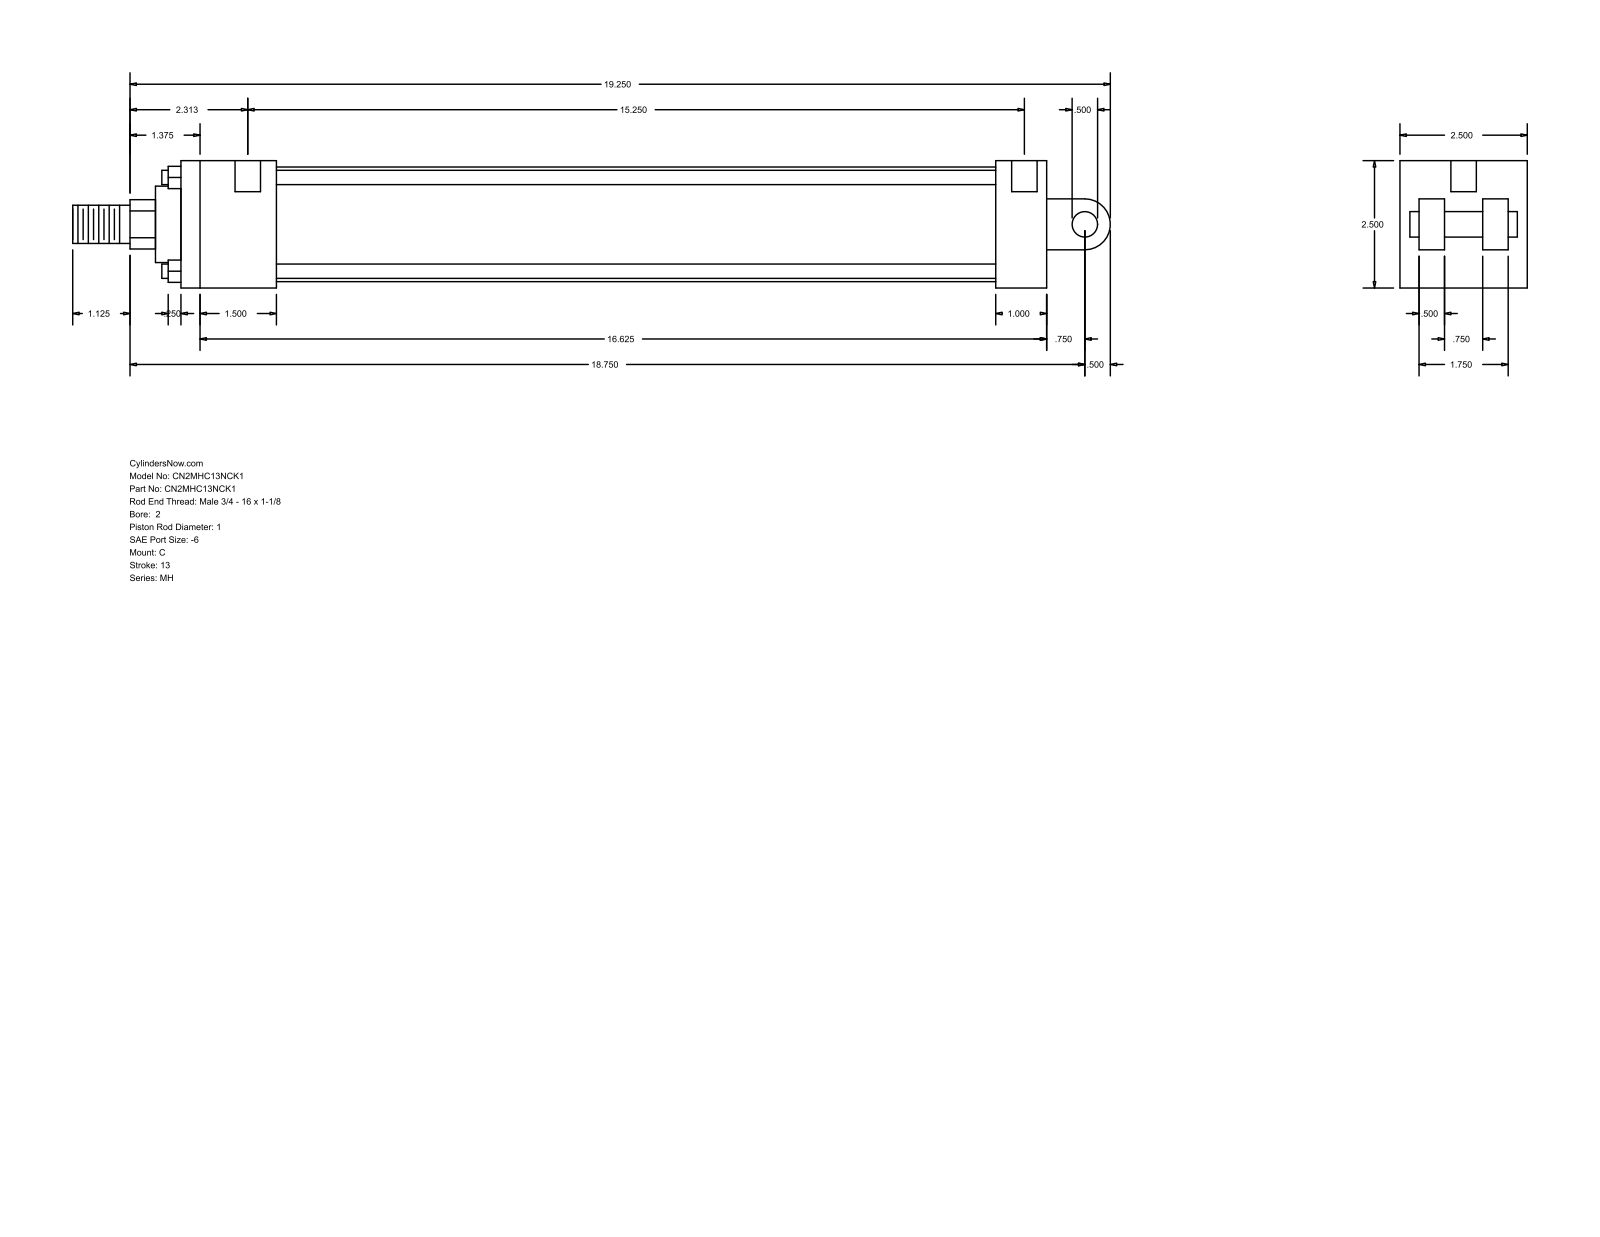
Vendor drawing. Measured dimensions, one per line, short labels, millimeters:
name: MH_C__0200_1
written by: GSSL Pune (CONFIG_CONTROL_DESIGN)
unit: mm
bodies: 0 solids, 99 faces (70 planar, 29 cylindrical, 0 other)
size: 517.52 × 63.5 × 63.5
holes: 4× ⌀5.56, 2× ⌀12.7
bosses: 4× ⌀7.14, 1× ⌀57.15, 1× ⌀38.1, 1× ⌀25.4, 1× ⌀19.05, 1× ⌀12.7
rounds: 1× R12.29, 1× R12.7
face distances: 63.5, 431.8, 12.7, 25.4, 47.63, 53.98, 9.52, 406.4, 358.77, 384.17
hole spacings: 395.28, 3.17, 4.76, 387.35, 390.52, 392.11
